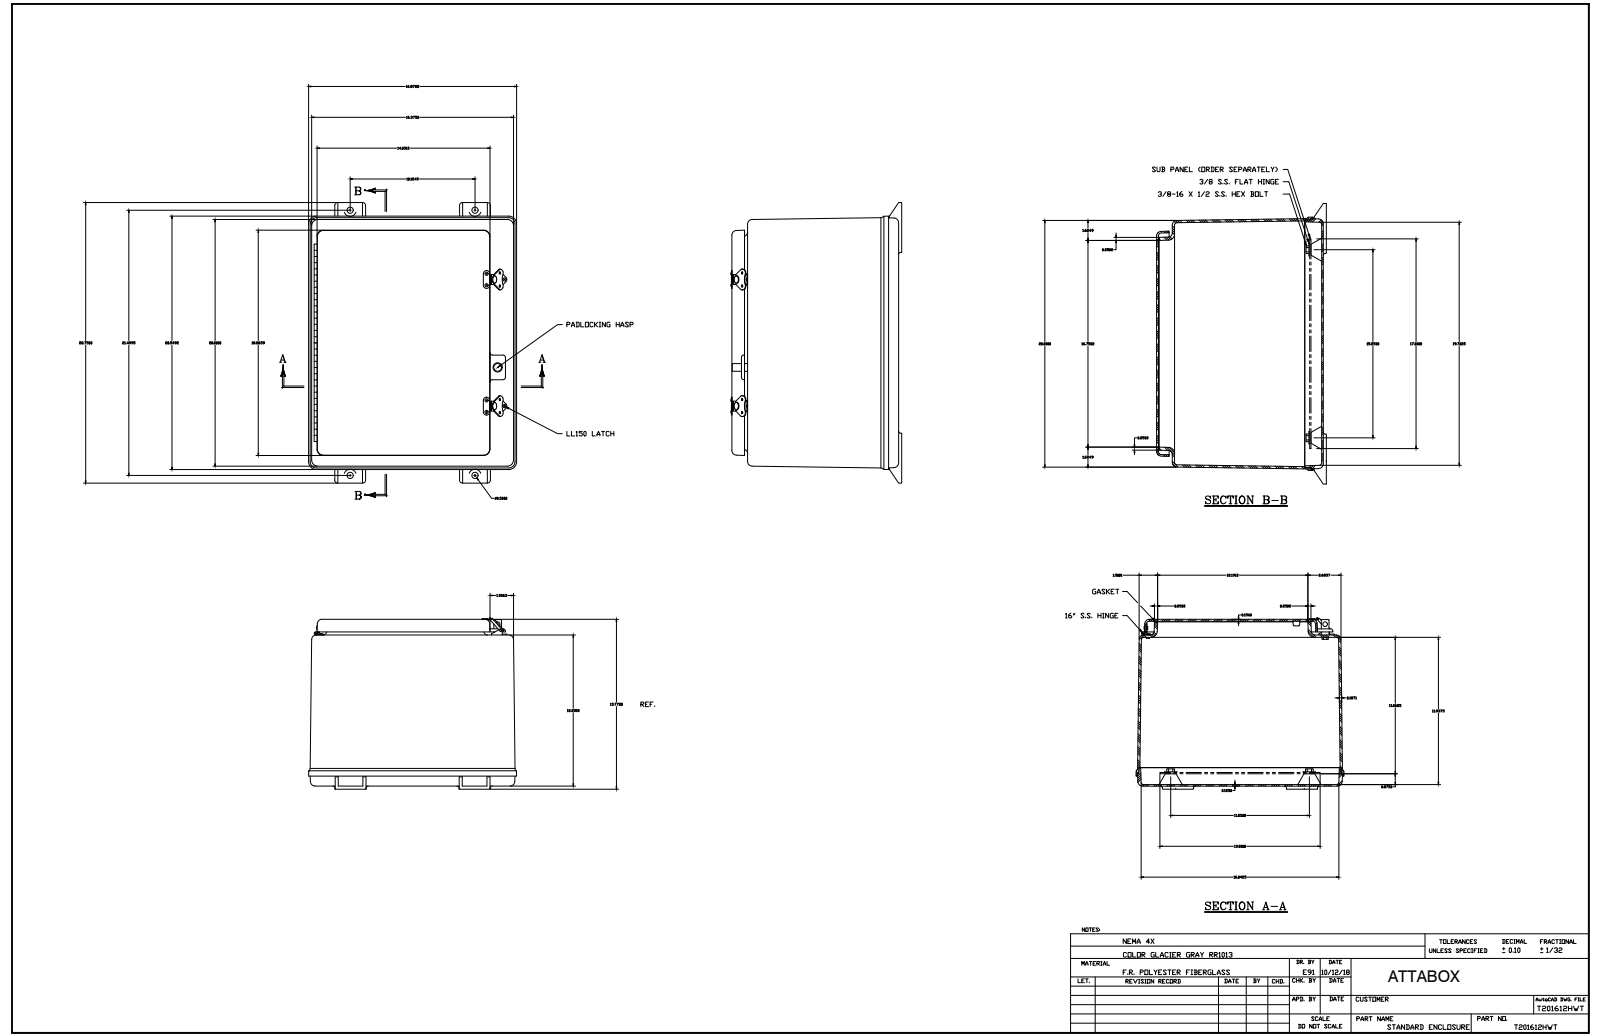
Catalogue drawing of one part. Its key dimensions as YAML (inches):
part_name: "T201612HWT"
step_written_by: "SolidWorks 2018 (AUTOMOTIVE_DESIGN)"
units: inches
bodies: {solids: 38, faces: 1100, planar: 419, cylindrical: 430, other: 251}
overall_size: [22.75, 16.875, 13.955]
volume: 312.5
surface_area: 3673
round_holes:
  - {diameter: 0.13, count: 20}
  - {diameter: 0.063, count: 8}
  - {diameter: 0.065, count: 5}
  - {diameter: 0.138, count: 4}
  - {diameter: 0.187, count: 4}
  - {diameter: 0.563, count: 4}
  - {diameter: 0.065, count: 3}
  - {diameter: 0.281, count: 2}
  - {diameter: 0.51, count: 2}
  - {diameter: 0.51, count: 2}
  - {diameter: 0.125, count: 1}
  - {diameter: 0.135, count: 1}
round_bosses_or_shafts:
  - {diameter: 0.297, count: 8}
  - {diameter: 0.14, count: 8}
  - {diameter: 0.5, count: 2}
  - {diameter: 0.25, count: 1}
  - {diameter: 0.201, count: 1}
  - {diameter: 0.2, count: 1}
partial_cylinders:
  - {radius: 0.01, count: 59}
  - {radius: 0.25, count: 24}
  - {radius: 0.188, count: 19}
  - {radius: 0.5, count: 12}
  - {radius: 0.375, count: 10}
  - {radius: 0.03, count: 8}
  - {radius: 0.312, count: 8}
  - {radius: 0.187, count: 6}
face_to_face_distances: [0.187, 0.125, 0.156, 13.532, 13.407, 13.376, 13.25, 12.063, 11.937, 1.313]
hole_center_spacings: [10.25, 4.75, 5.5, 15, 1.527, 3.176, 10.25, 11.135]
